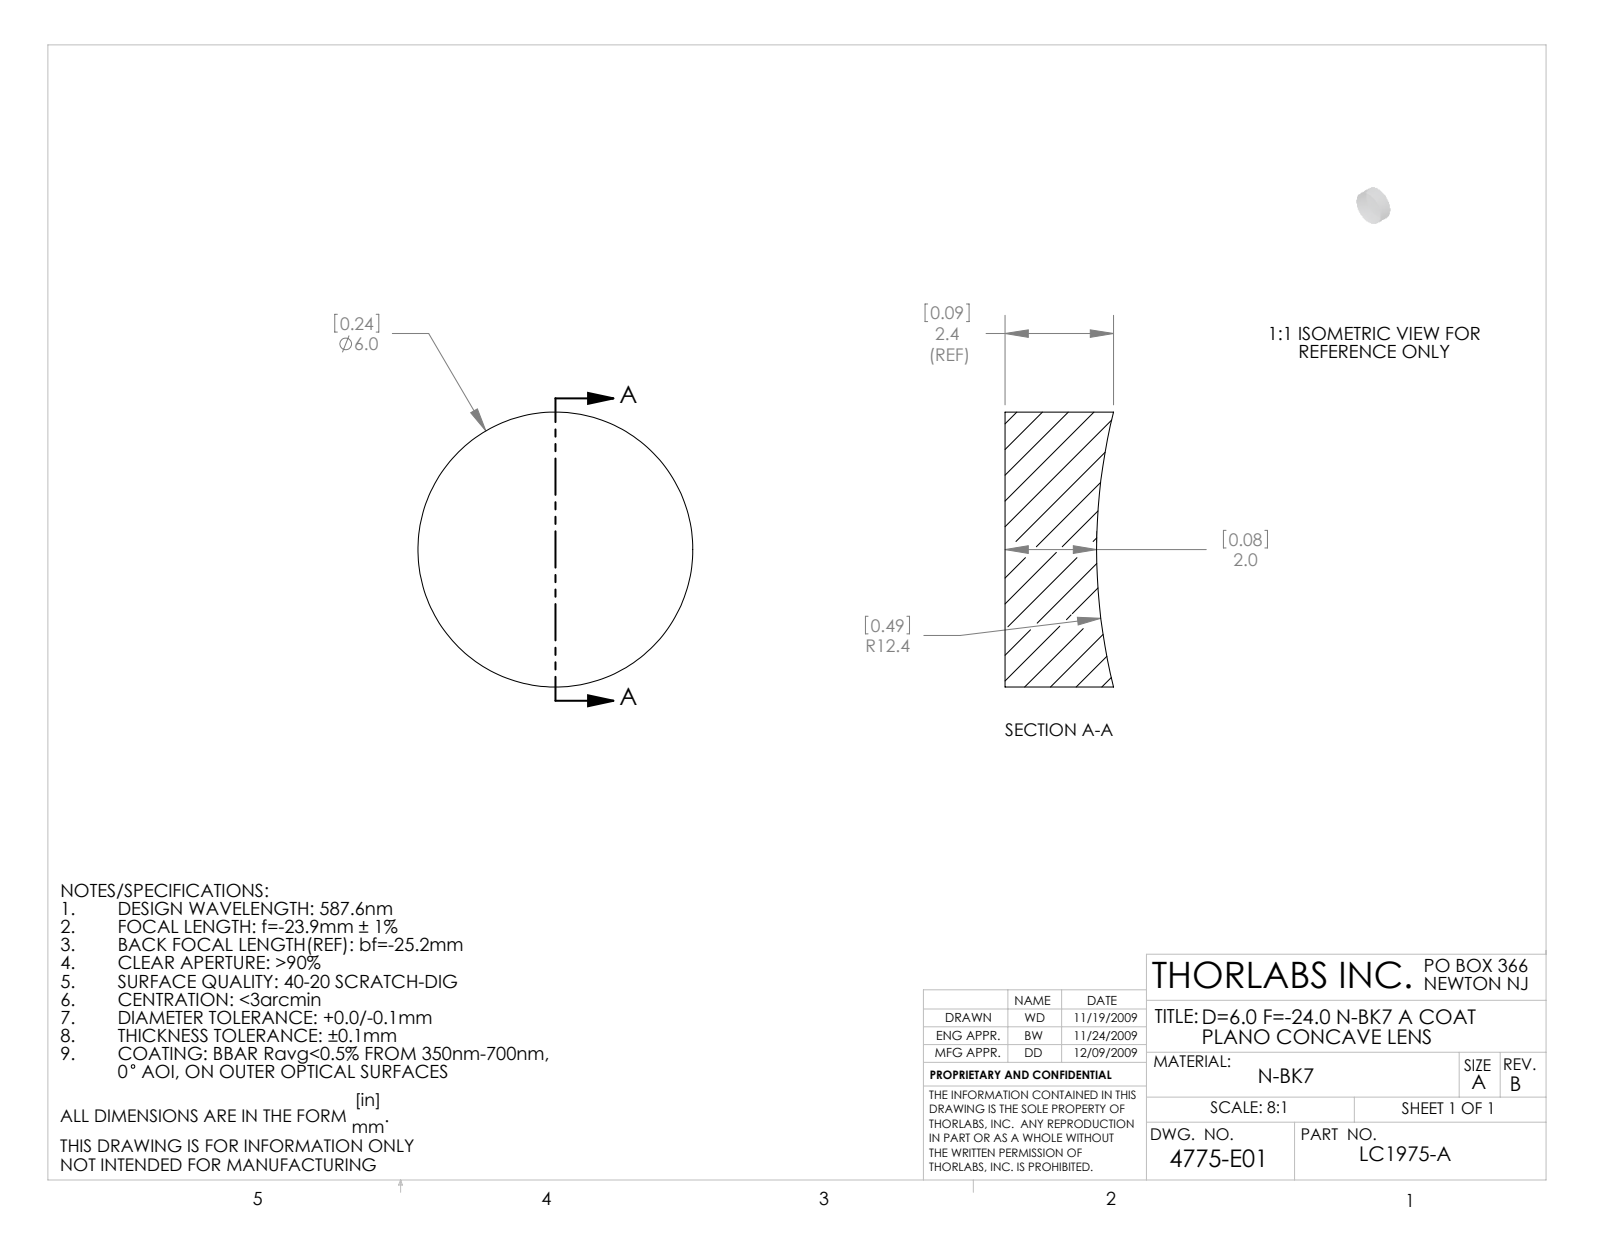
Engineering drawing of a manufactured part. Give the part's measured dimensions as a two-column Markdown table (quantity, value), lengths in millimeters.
| quantity | value |
| --- | --- |
| part name | 4775-E0W |
| STEP written by | SolidWorks 2009 (AUTOMOTIVE_DESIGN) |
| units | millimeters |
| bodies | 1 solid, 5 faces (1 planar, 2 cylindrical, 2 other) |
| overall size | 6 × 6 × 2.37 |
| volume | 62 mm³ |
| surface area | 102 mm² |
| round bosses / shafts (diameter × count) | 6 × 1 |
